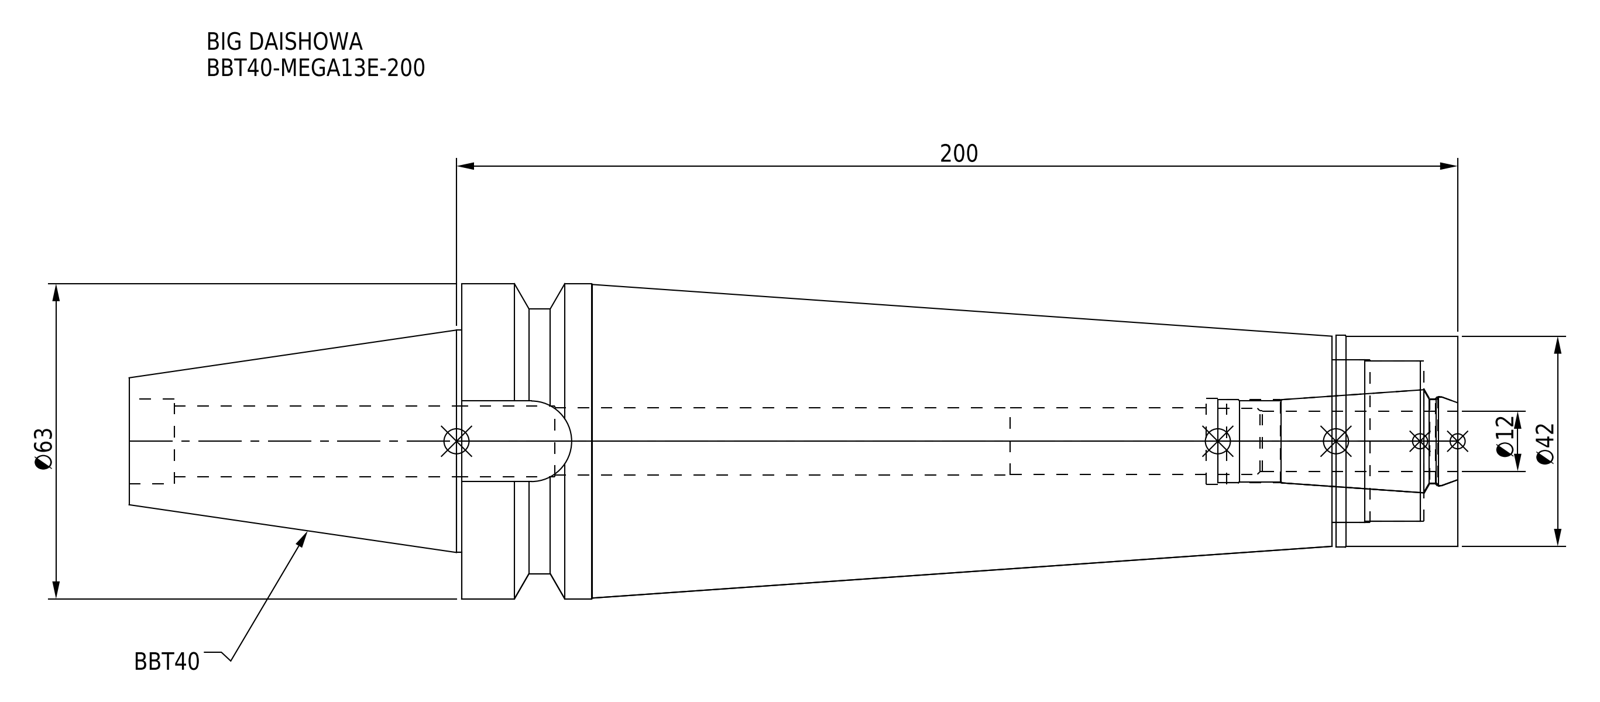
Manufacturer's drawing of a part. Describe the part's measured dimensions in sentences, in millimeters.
The part is named "BBT40-MEGA13E-200_1.stp; BBT40-MEGA13E-200-120.stp; DXF_TEMP_ASSY_ASM_4_ASM.stp; BBT40-MEGA13E-200-120-FreeParts (+3 more)". Its 3-D file was written by "SolidWorks 2019 (CONFIG_CONTROL_DESIGN)". It is 2 solids with 81 faces: 21 planar, 40 cylindrical and 20 other. Overall it measures 265.4 by 63 by 63 millimeters. Its volume is 446 758 cubic millimeters and its surface area 62 381 square millimeters. Round holes: 1 of diameter 13.3, 1 of diameter 13.5, 1 of diameter 14.2, 1 of diameter 16.6, 1 of diameter 17, 1 of diameter 17.2, 1 of diameter 17.9, 1 of diameter 32, 1 of diameter 32.5. Round bosses or shafts: 1 of diameter 63, 1 of diameter 53, 1 of diameter 44.45, 1 of diameter 42.3, 1 of diameter 42. Partial cylindrical surfaces (rounded edges, fillets, slot ends): 1 of radius 8.05. The main face-to-face distances are 199, 25.1, 24.3, 174.7, 0.8, 173.9, 6.8, 17.5, 7.5, 16.8.
